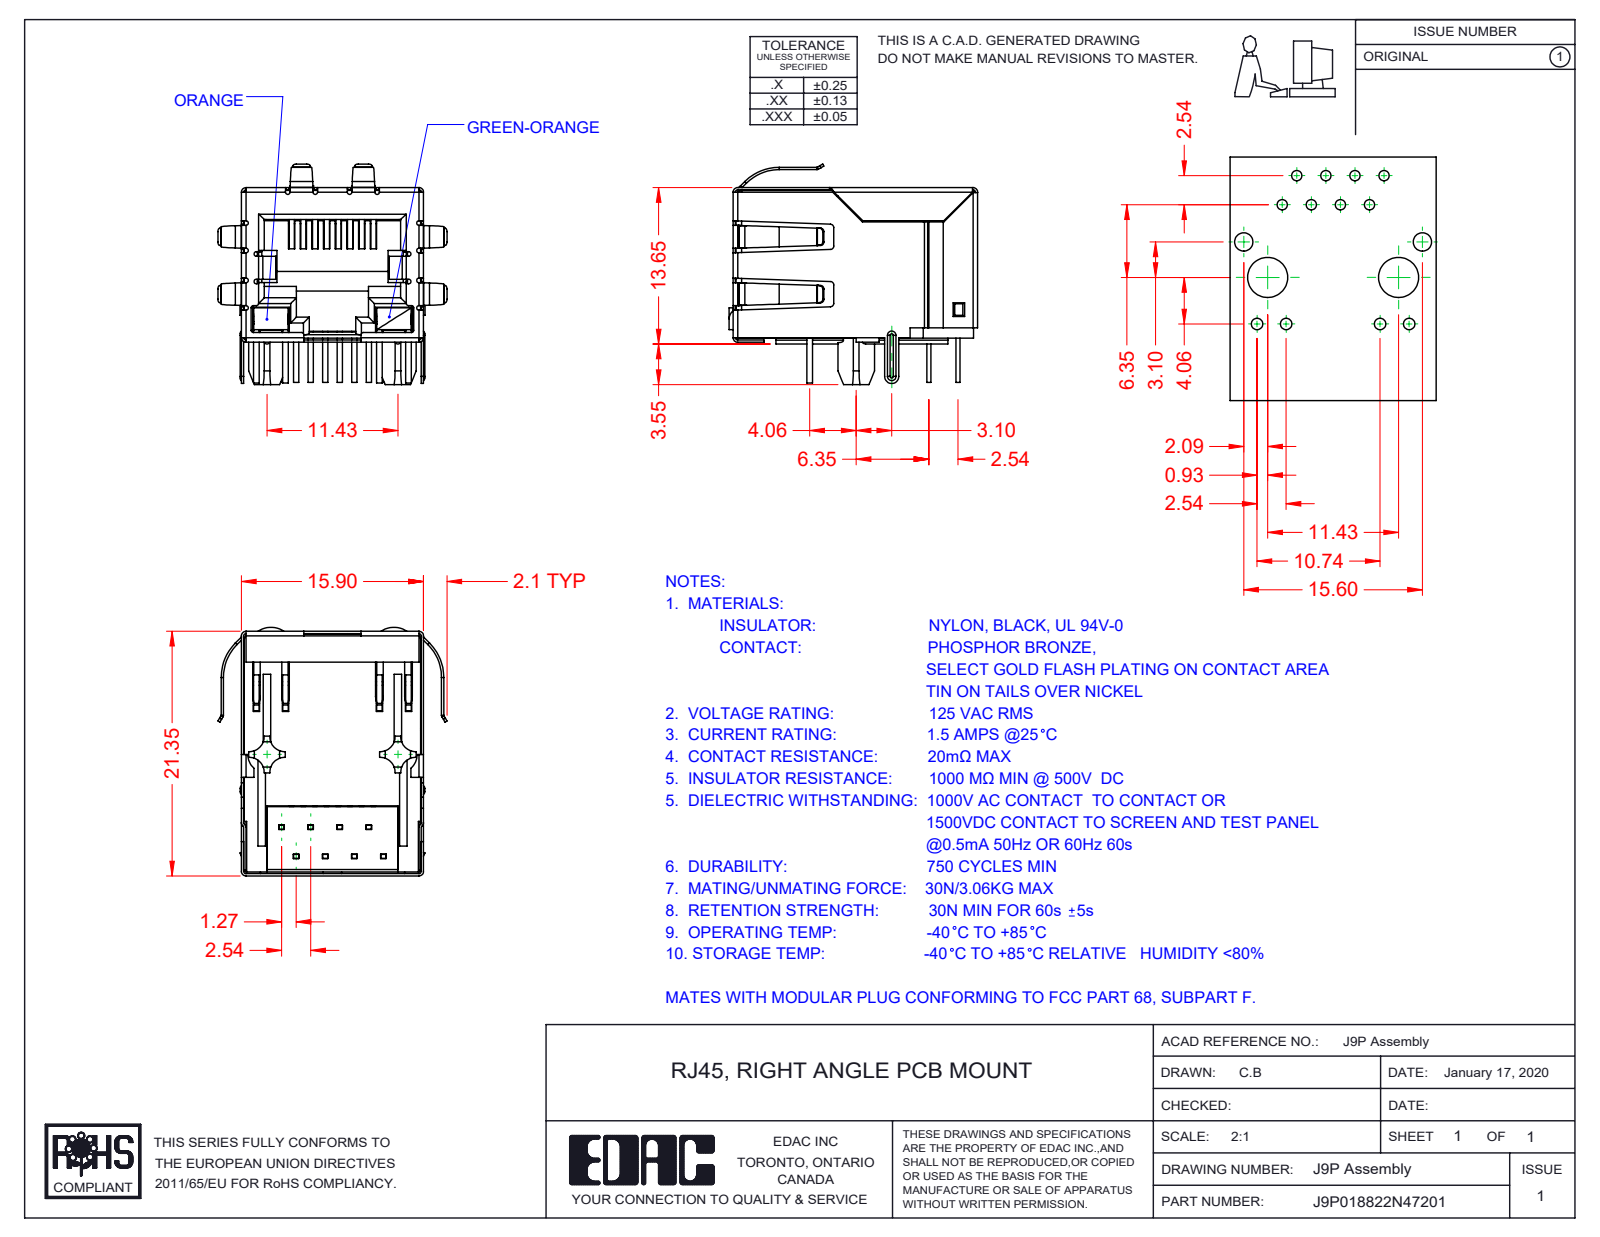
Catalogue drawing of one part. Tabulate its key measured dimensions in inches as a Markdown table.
| quantity | value |
| --- | --- |
| part name | J9P018822N47202; 9P-LED Contacts; 9P-LED LED RH_7-Green-Orange; 9P-LED Contact Lock (+4 more) |
| STEP written by | SolidWorks 2016 (CONFIG_CONTROL_DESIGN) |
| units | inches |
| bodies | 13 solids, 1474 faces (1042 planar, 338 cylindrical, 94 other) |
| overall size | 0.854 × 0.787 × 0.758 |
| volume | 0.164 in³ |
| surface area | 11.65 in² |
| partial cylindrical surfaces (radius × count) | 0.008 × 39, 0.02 × 22, 0.012 × 20, 0.016 × 16, 0.051 × 8, 0.009 × 5, 0.004 × 4, 0.012 × 4 |
| main face-to-face distances | 0.608, 0.618, 0.616, 0.014, 0.021, 0.61, 0.487, 0.024, 0.055, 0.023 |
